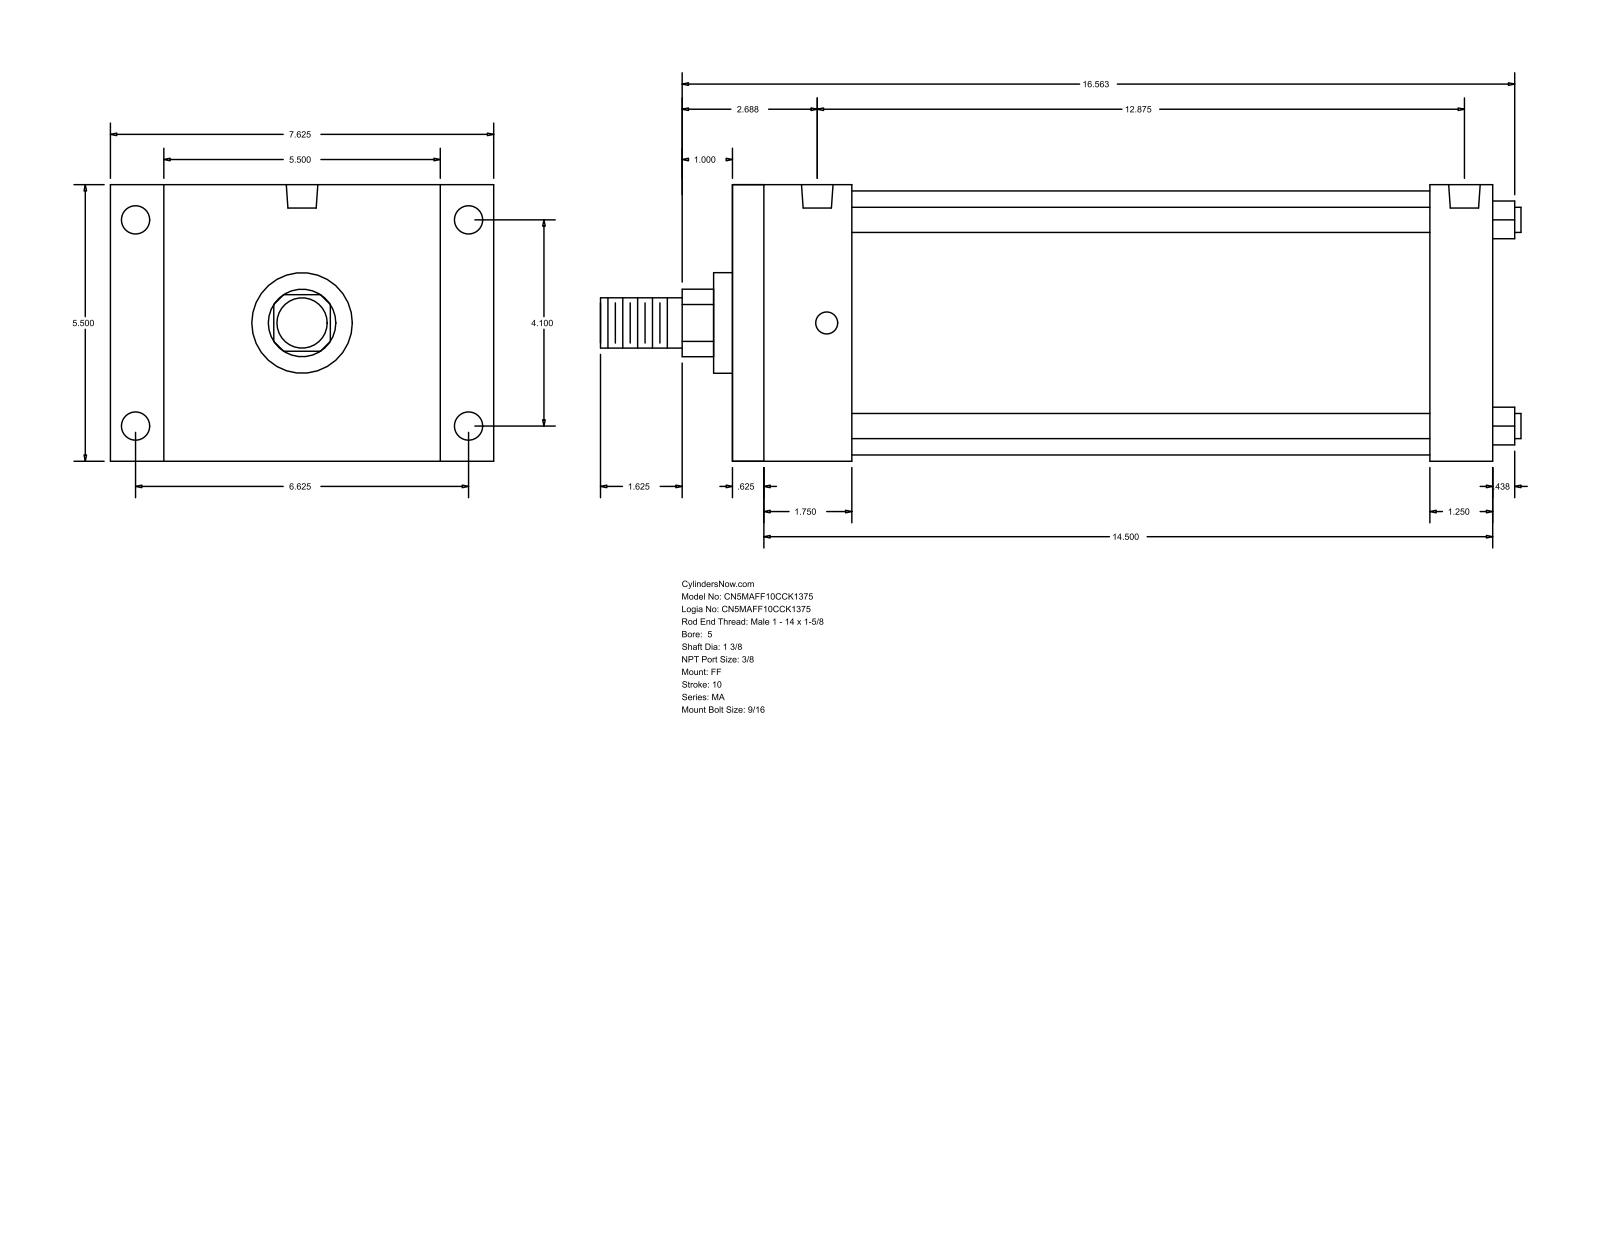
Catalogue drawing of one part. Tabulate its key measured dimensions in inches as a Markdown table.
| quantity | value |
| --- | --- |
| part name | MA_FF__0500_1.375 |
| STEP written by | GSSL Pune (CONFIG_CONTROL_DESIGN) |
| units | inches |
| bodies | 0 solids, 92 faces (64 planar, 28 cylindrical, 0 other) |
| overall size | 18.313 × 7.625 × 5.5 |
| round holes (diameter × count) | 0.437 × 4, 0.563 × 4, 0.627 × 2 |
| round bosses / shafts (diameter × count) | 0.5 × 4, 5.25 × 1, 2 × 1, 1.375 × 1, 1 × 1 |
| partial cylindrical surfaces (radius × count) | 0.672 × 1 |
| main face-to-face distances | 5.5, 15.125, 0.625, 14.5, 13.875, 13.25, 1.25, 2.375, 1.75, 11.5 |
| hole center spacings | 0.188, 4.1, 6.625, 7.791, 12.5, 12.687, 12.875 |
